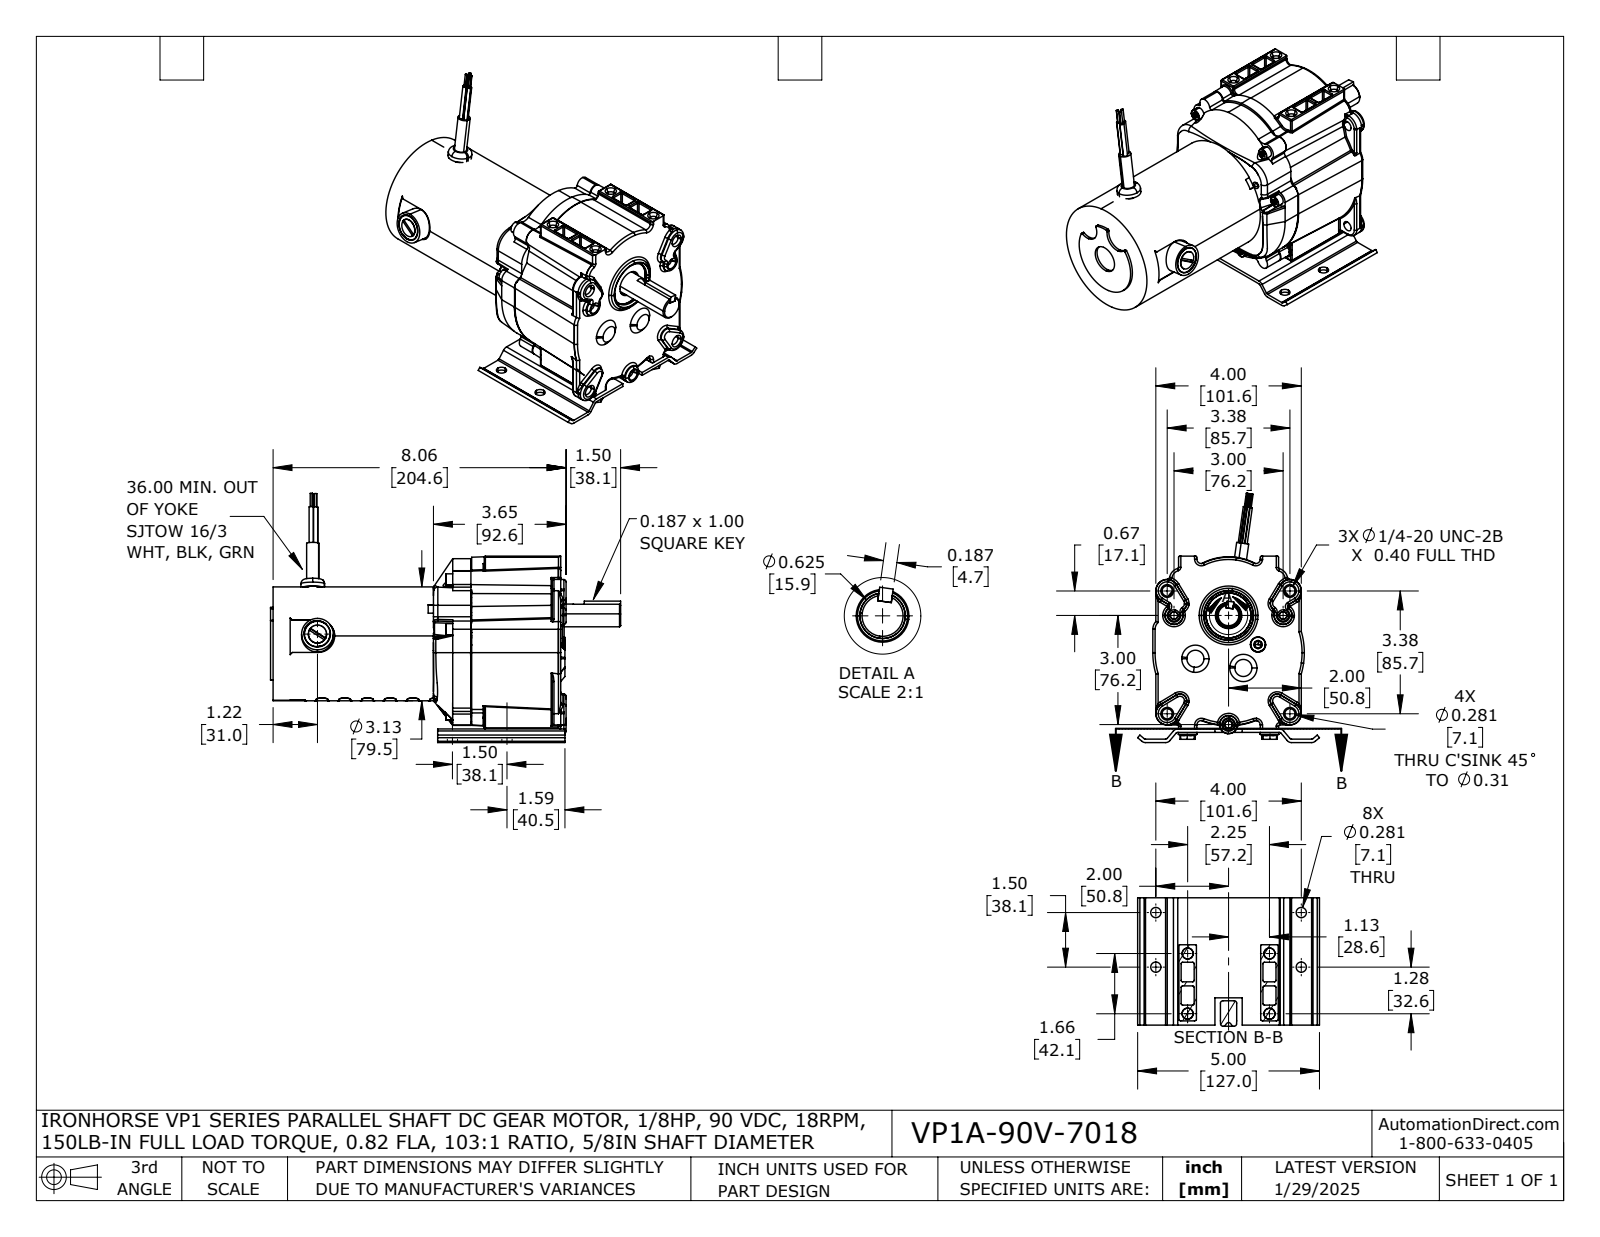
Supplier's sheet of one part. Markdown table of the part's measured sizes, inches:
| quantity | value |
| --- | --- |
| part name | VP1A-90V-7018 |
| STEP written by | SolidWorks 2024 (AUTOMOTIVE_DESIGN) |
| units | inches |
| bodies | 8 solids, 2435 faces (642 planar, 688 cylindrical, 1105 other) |
| overall size | 9.627 × 6.854 × 5 |
| volume | 82.44 in³ |
| surface area | 303.9 in² |
| round holes (diameter × count) | 0.281 × 12, 0.218 × 5, 0.207 × 3, 0.135 × 2, 0.159 × 2, 0.166 × 2, 0.204 × 2, 0.397 × 2, 0.688 × 2, 0.75 × 1, 0.813 × 1, 0.875 × 1 |
| round bosses / shafts (diameter × count) | 0.307 × 5, 0.19 × 5, 0.51 × 4, 0.3 × 4, 0.12 × 3, 0.06 × 3, 0.873 × 2, 0.733 × 2 |
| partial cylindrical surfaces (radius × count) | 0.03 × 52, 0.031 × 38, 0.062 × 22, 0.12 × 18, 0.156 × 13, 0.19 × 10, 0.05 × 8, 0.06 × 7 |
| main face-to-face distances | 2.449, 3.5, 1.051, 0.095, 0.095, 7.91, 5.461, 4.41, 0.13, 0.28 |
| hole center spacings | 1.5, 1.691, 0.698, 0.952, 1.224, 1.426, 1.552, 1.656 |
